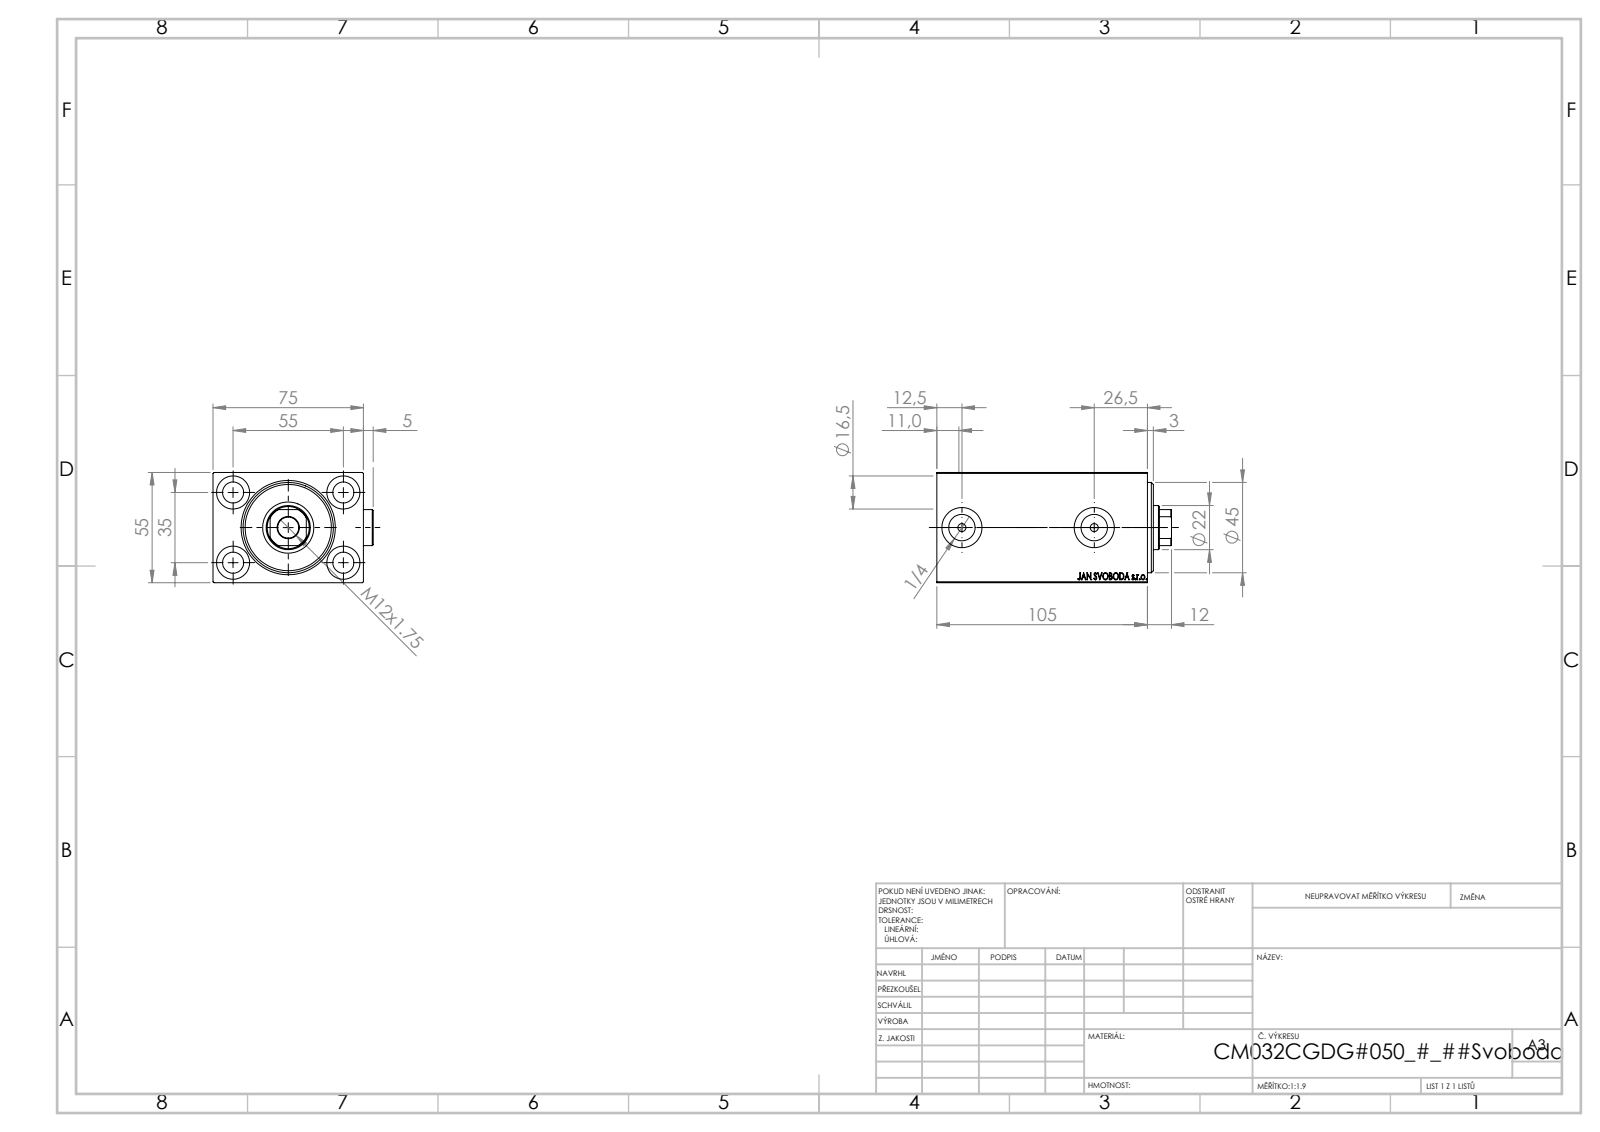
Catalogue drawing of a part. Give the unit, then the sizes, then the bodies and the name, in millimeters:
Units: millimetres
Overall size (bounding box): 117 × 79.9 × 55
Round holes (diameter × count): ⌀10.5 ×5, ⌀16.5 ×4, ⌀4 ×2, ⌀13.16 ×2, ⌀20 ×2, ⌀22 ×1, ⌀25.5 ×1, ⌀32 ×1, ⌀34 ×1, ⌀45 ×1
Round bosses / shafts (diameter × count): ⌀18 ×2
Partial cylindrical surfaces — rounded edges, fillets, slot ends (radius × count): R10.5 ×1
Main face-to-face distances: 55, 75, 5, 10, 95, 105, 100, 90, 74.9, 83
Hole centre spacings: 32.6, 35, 55, 65.19, 66
Volume: 364 796 mm³ · Surface area: 80 102 mm²
Bodies: 5 solids, 916 faces (442 planar, 76 cylindrical, 398 other)
Part name (STEP PRODUCT): Zatka_OIL_PORT; V450CM_C_VCP; V450CM_C_Body; V450CM_VC_B
STEP written by: SolidWorks 2019 (CONFIG_CONTROL_DESIGN)
